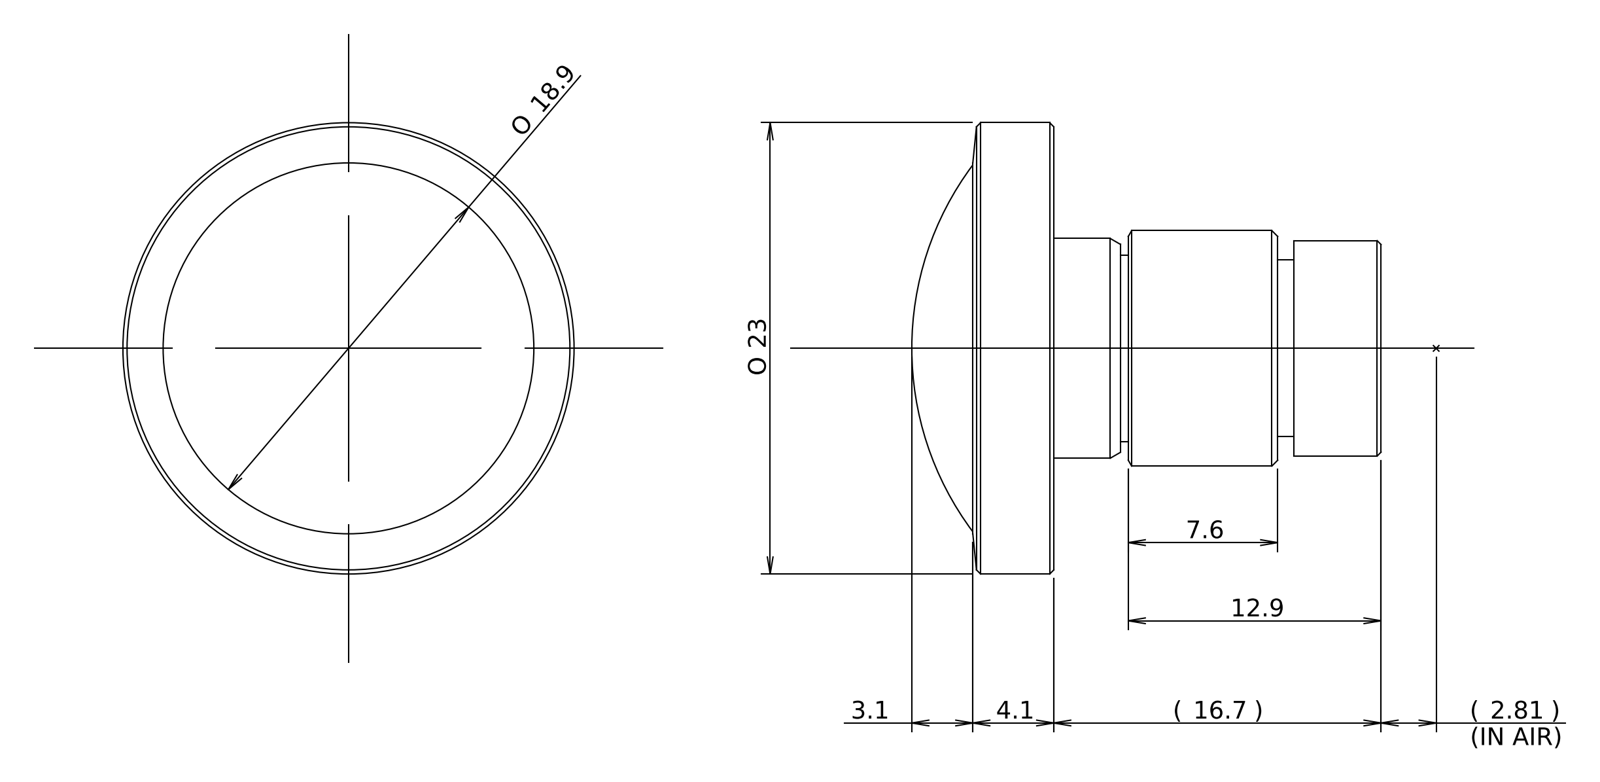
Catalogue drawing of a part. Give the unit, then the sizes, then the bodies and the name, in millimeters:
Units: millimetres
Overall size (bounding box): 23.92 × 23 × 23
Round holes (diameter × count): ⌀5.74 ×1, ⌀18.9 ×1
Round bosses / shafts (diameter × count): ⌀23 ×1, ⌀12 ×1, ⌀11.2 ×1, ⌀10.97 ×1, ⌀9.5 ×1, ⌀9 ×1
Main face-to-face distances: 11.42, 3.8, 7.62, 12.25, 8.45, 0.83, 16.59, 12.79, 5.17, 4.34
Volume: 3 780 mm³ · Surface area: 1 869 mm²
Bodies: 1 solid, 26 faces (8 planar, 8 cylindrical, 10 other)
Part name (STEP PRODUCT): TLB-2000-IRCF_20210604
STEP written by: ST-DEVELOPER v16.7 (AUTOMOTIVE_DESIGN)
